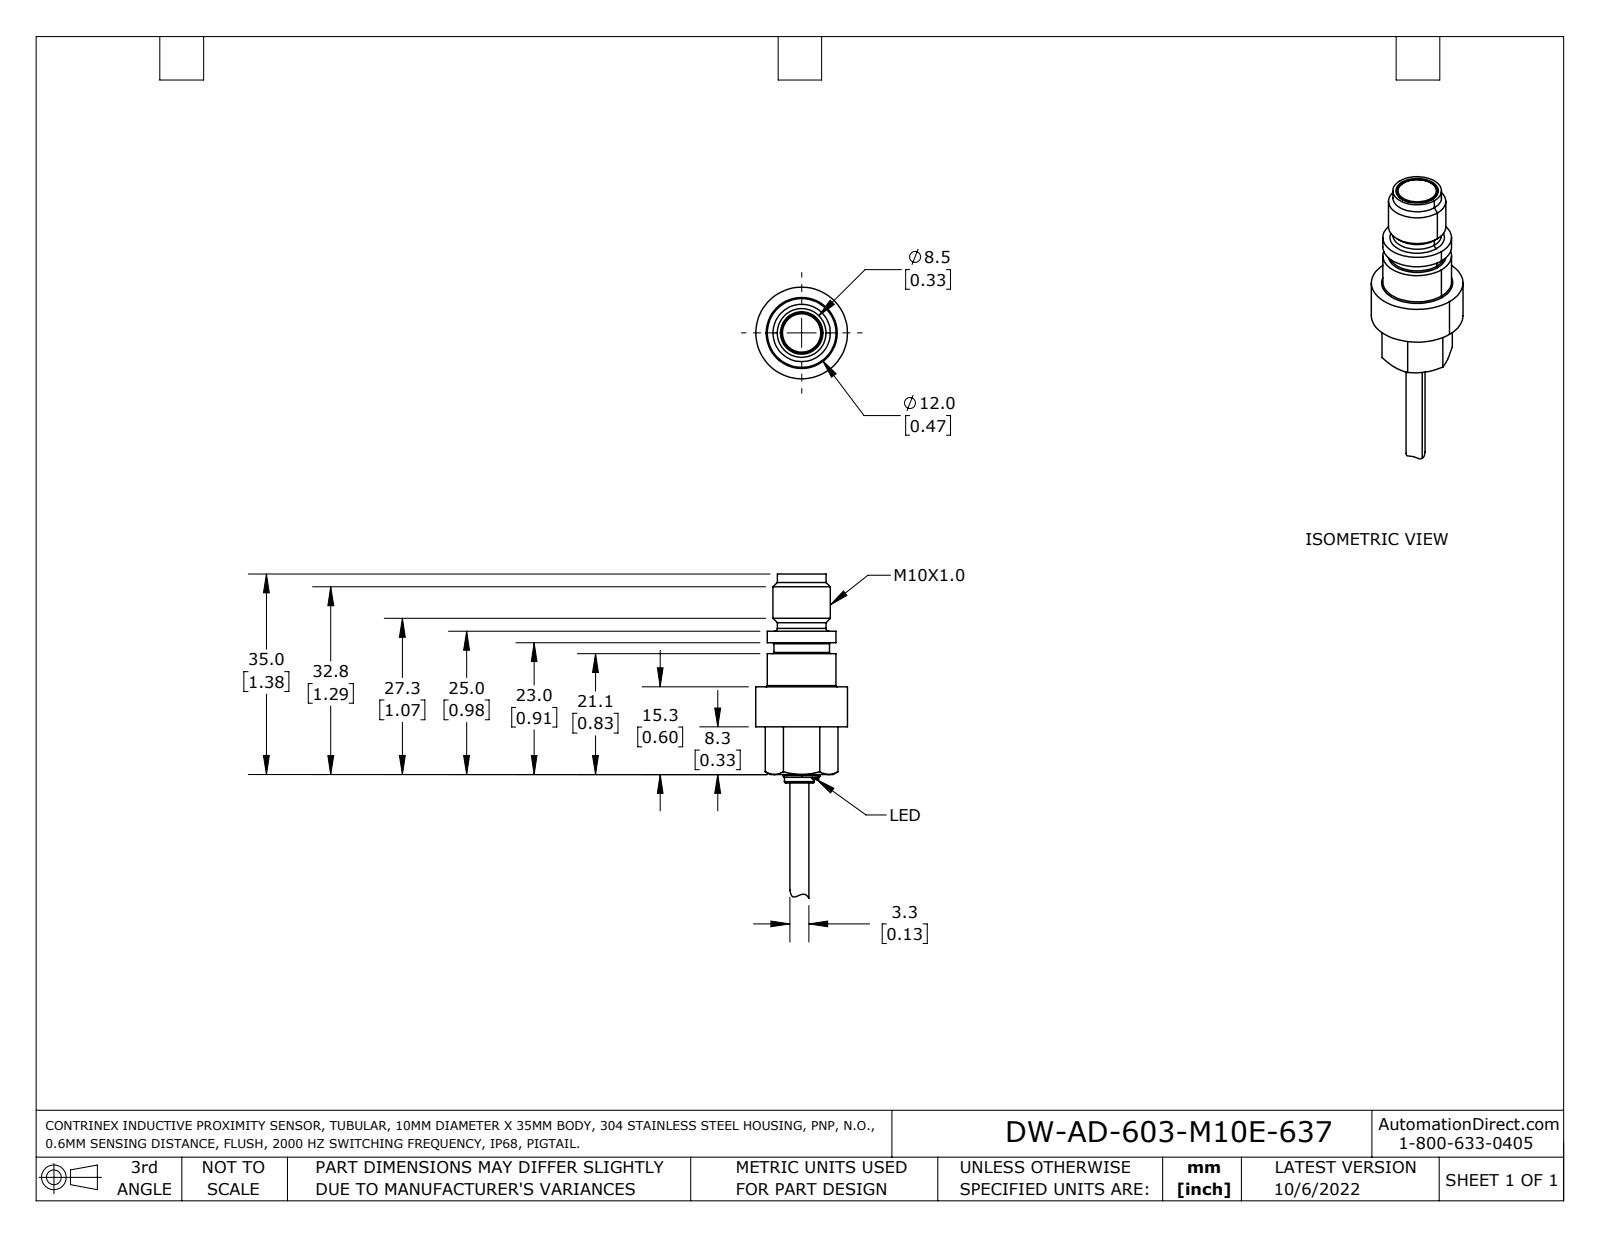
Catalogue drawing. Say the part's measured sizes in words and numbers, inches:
The part is named "DW-AD-603-M10E-637". Its 3-D file was written by "SolidWorks 2021 (AUTOMOTIVE_DESIGN)". It is 1 solid with 99 faces: 43 planar, 24 cylindrical and 32 other. Overall it measures 2.228 by 0.63 by 0.63 inches. Its volume is 0.257 cubic inches and its surface area 3.144 square inches. Round bosses or shafts: 1 of diameter 0.63, 1 of diameter 0.472, 1 of diameter 0.394, 1 of diameter 0.382, 1 of diameter 0.335, 1 of diameter 0.276, 1 of diameter 0.256, 1 of diameter 0.205. Partial cylindrical surfaces (rounded edges, fillets, slot ends): 2 of radius 0.012, 1 of radius 0.116. The main face-to-face distances are 0.433, 0.276, 0.602, 0.327, 0.776, 1.051, 1.378, 0.394, 0.382, 0.657.
